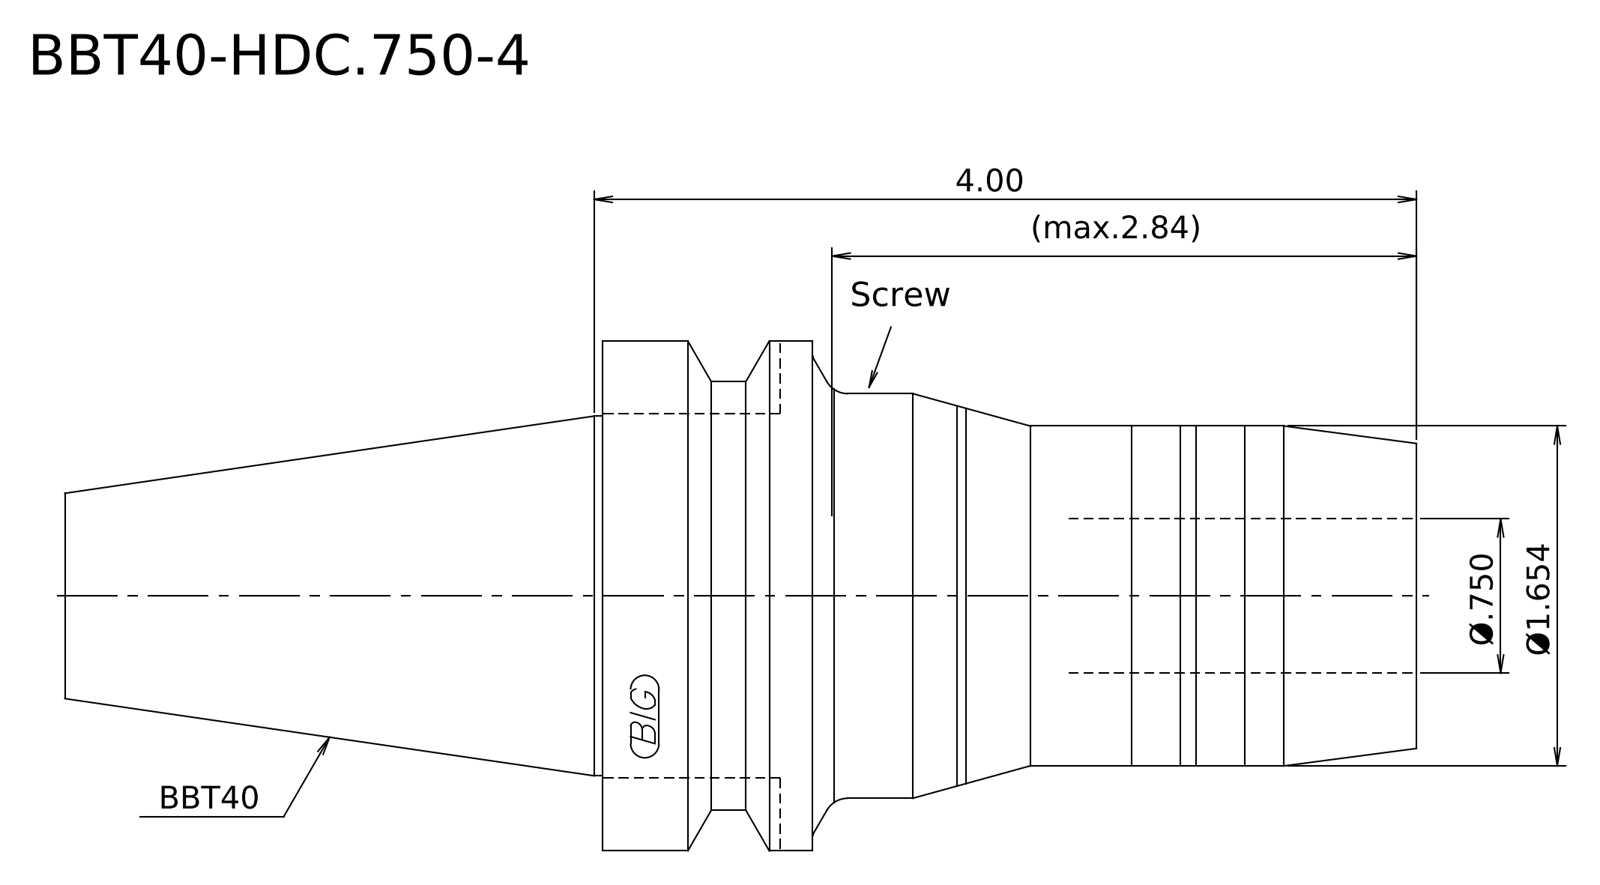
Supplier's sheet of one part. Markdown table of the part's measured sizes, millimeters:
| quantity | value |
| --- | --- |
| STEP written by | Kubotek KeyCreator 2011 V10.0.2 (22737) (automotive_design) |
| units | millimeters |
| bodies | 1 solid, 16 faces (4 planar, 6 cylindrical, 6 other) |
| overall size | 167 × 63 × 63 |
| volume | 254 173 mm³ |
| surface area | 27 633 mm² |
| round bosses / shafts (diameter × count) | 63 × 1, 53 × 1, 50 × 1, 44.45 × 1, 42 × 1 |
| main face-to-face distances | 100.6, 167, 66.4, 74.6, 26, 92.4 |
